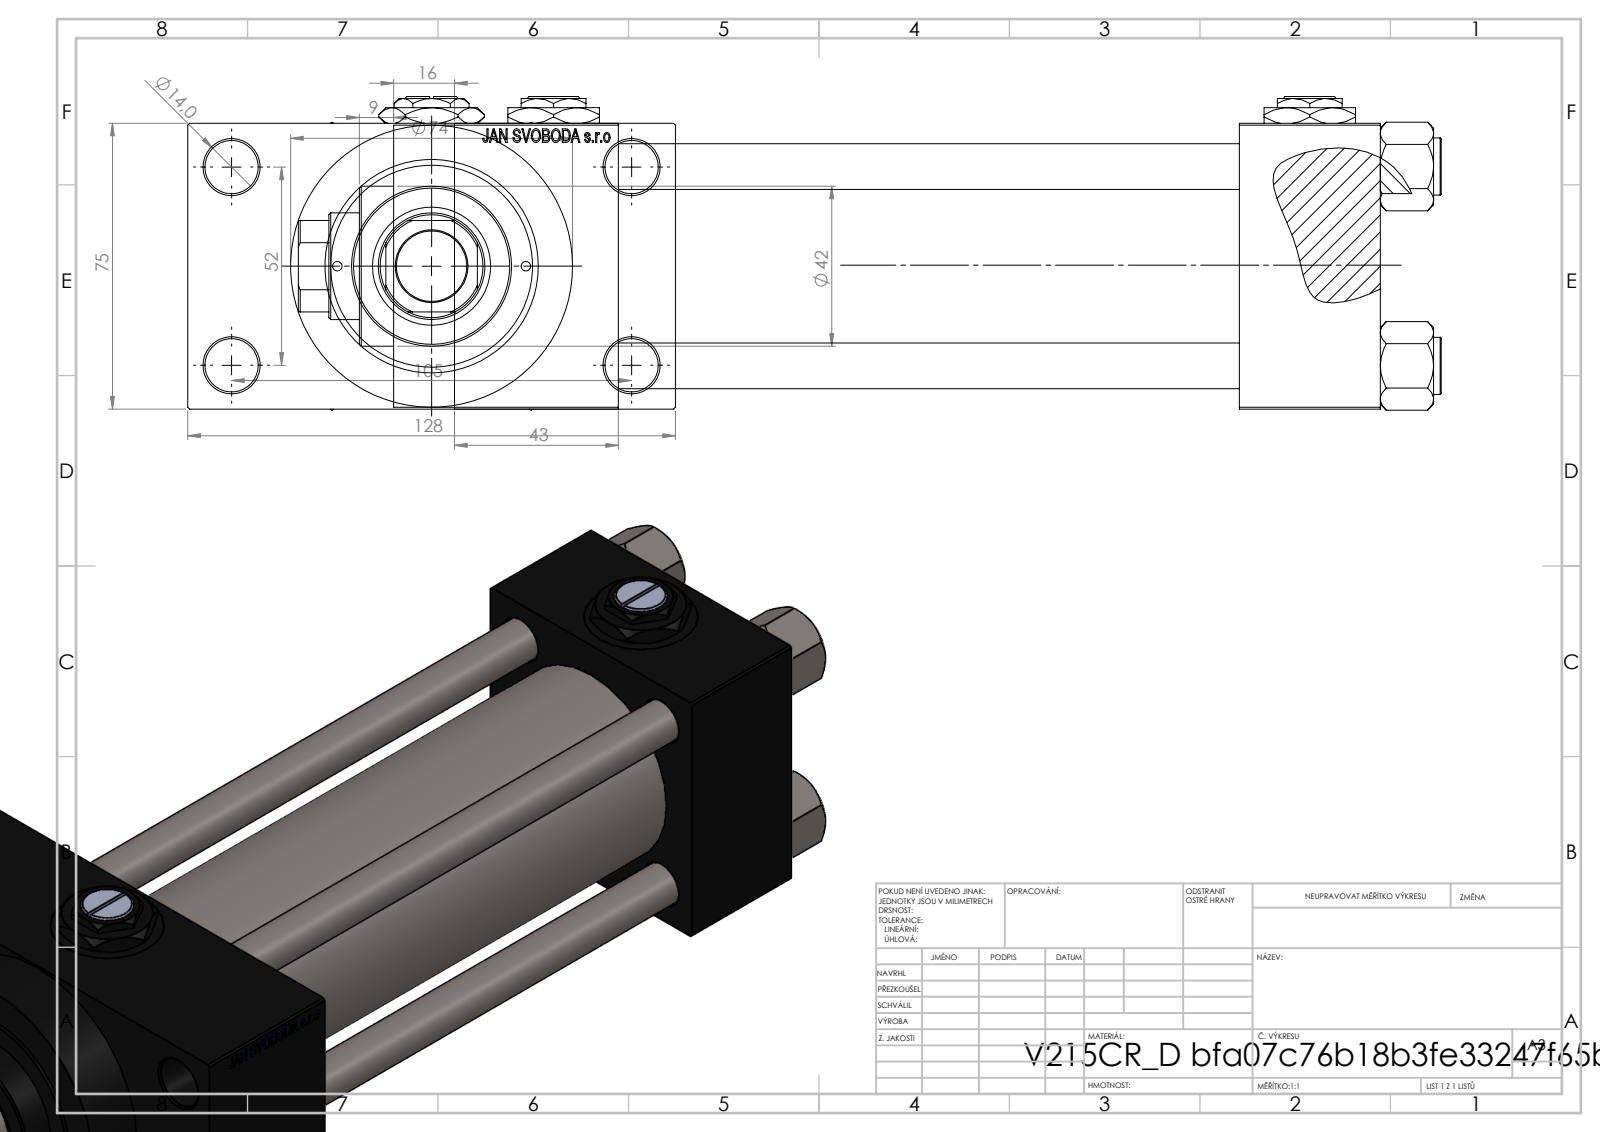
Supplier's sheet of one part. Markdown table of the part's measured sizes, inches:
| quantity | value |
| --- | --- |
| part name | V215CR_VCP_D; NUT_M5_D; V215CR_D_TYCINKA; V215CR_D_Body (+2 more) |
| STEP written by | SolidWorks 2019 (CONFIG_CONTROL_DESIGN) |
| units | inches |
| bodies | 13 solids, 1212 faces (547 planar, 103 cylindrical, 562 other) |
| overall size | 11.811 × 5.039 × 3.239 |
| volume | 58.96 in³ |
| surface area | 364 in² |
| round holes (diameter × count) | 0.472 × 4, 0.551 × 4, 0.825 × 4, 1.181 × 4, 0.276 × 3, 0.098 × 2, 0.728 × 1, 1.102 × 1, 1.22 × 1, 1.614 × 1, 1.969 × 1, 2.087 × 1 |
| round bosses / shafts (diameter × count) | 0.591 × 4, 2.913 × 1, 2.205 × 1, 1.654 × 1 |
| partial cylindrical surfaces (radius × count) | 0.531 × 1 |
| main face-to-face distances | 2.953, 6.417, 1.457, 7.874, 1.043, 9.567, 8.11, 1.693, 3.996, 0.63 |
| hole center spacings | 1.031, 1.037, 1.456, 1.497, 2.059, 2.253, 2.3, 2.307 |
